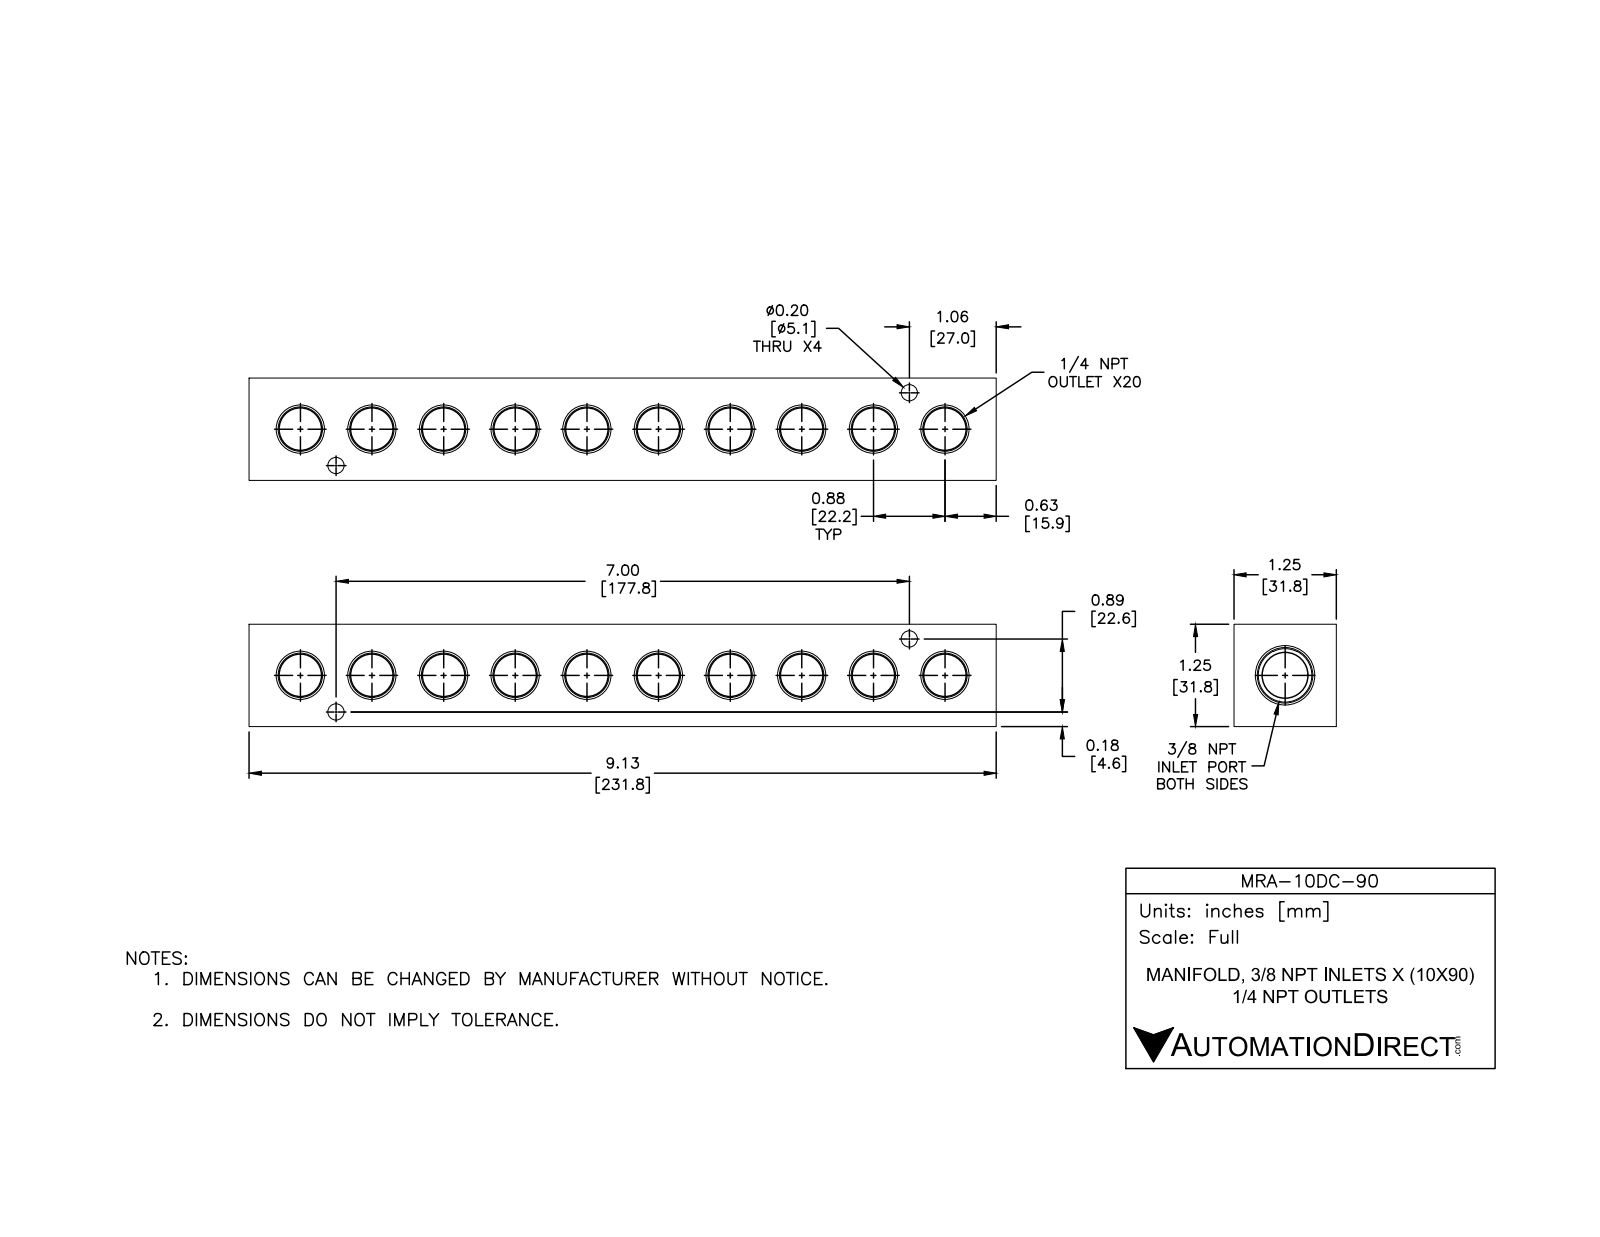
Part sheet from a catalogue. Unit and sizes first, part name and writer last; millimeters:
Units: millimetres
Overall size (bounding box): 231.8 × 31.8 × 31.8
Round holes (diameter × count): ⌀5.1 ×4, ⌀14.3 ×1
Partial cylindrical surfaces — rounded edges, fillets, slot ends (radius × count): R5.6 ×20
Main face-to-face distances: 31.8, 231.8, 21.8, 9.9, 10.4, 221.4, 210.9
Hole centre spacings: 179.2
Volume: 165 800 mm³ · Surface area: 46 190 mm²
Bodies: 1 solid, 198 faces (50 planar, 60 cylindrical, 88 other)
Part name (STEP PRODUCT): MRA-10DC-90
STEP written by: SolidWorks 2015 (CONFIG_CONTROL_DESIGN)
